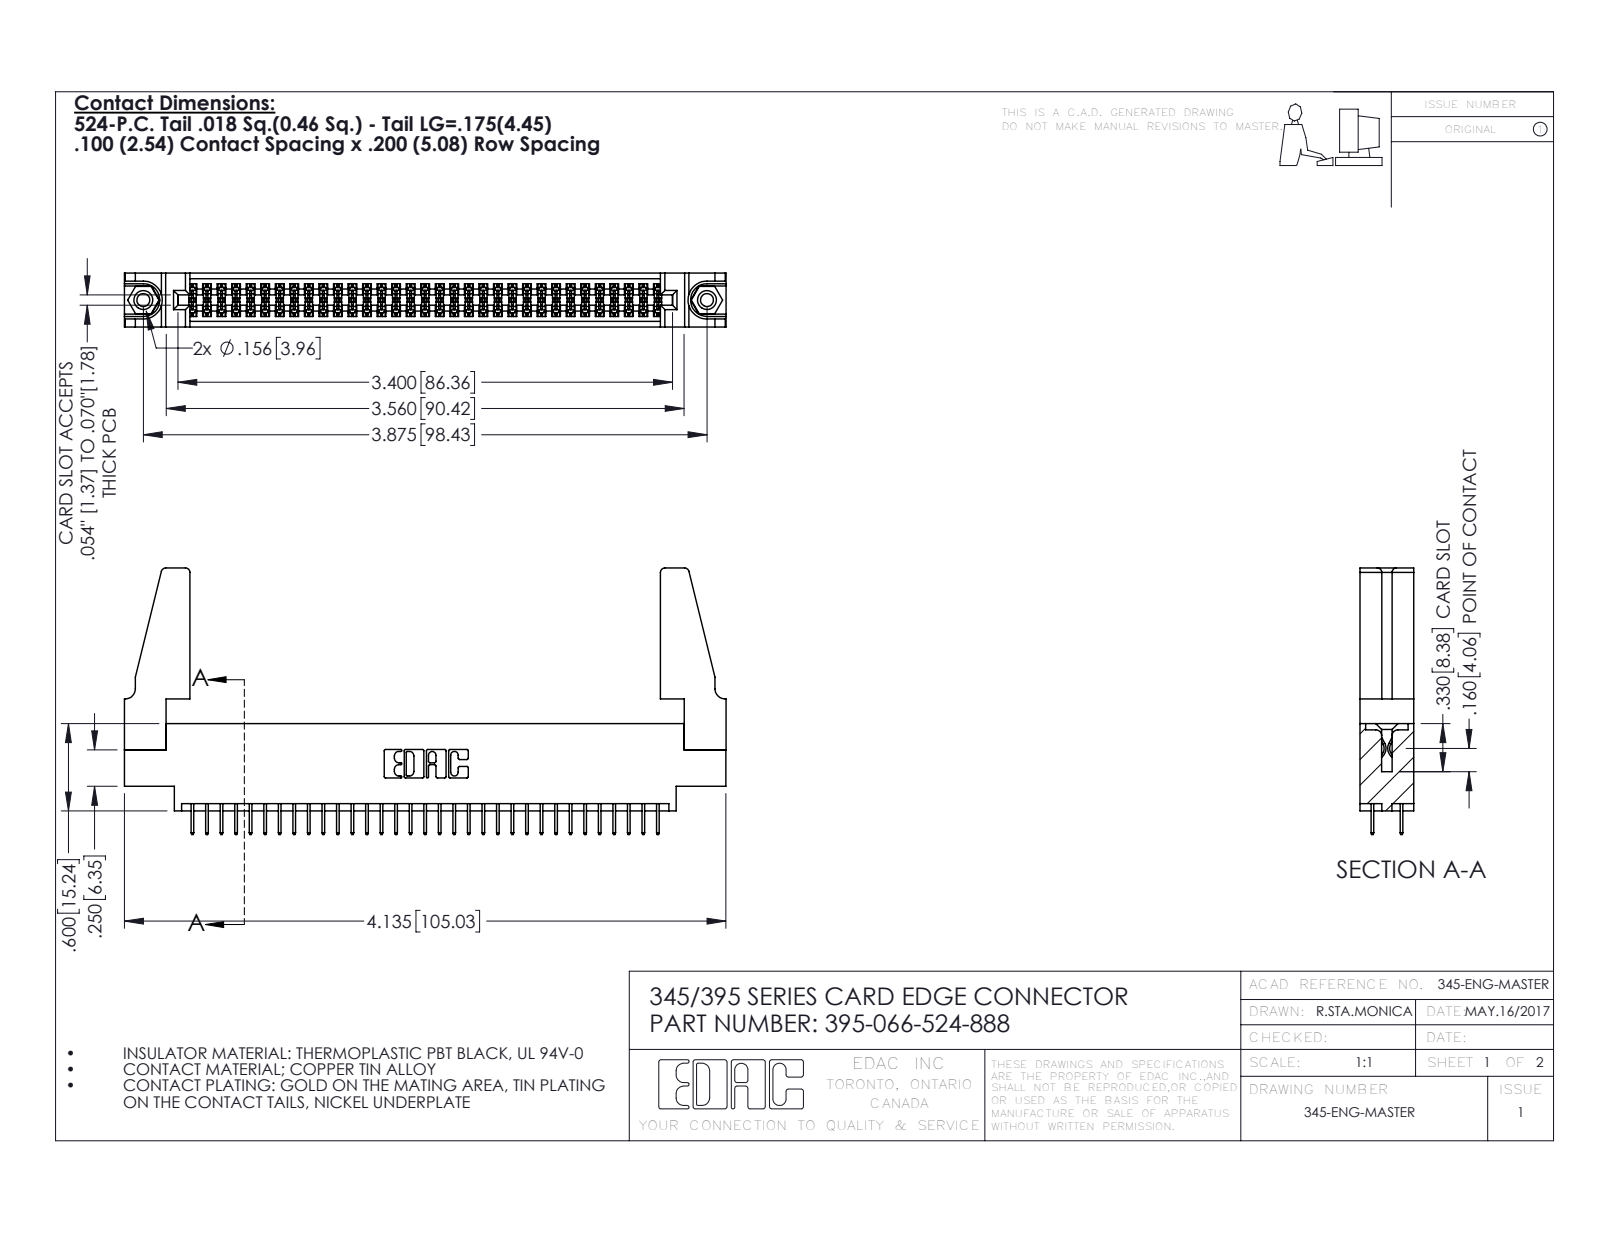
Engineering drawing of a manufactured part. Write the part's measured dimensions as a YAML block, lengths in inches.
part_name: "395-066-524-888; 345-292-001_345-293-124; 345-220-078_345-220-088; 345-250-001_345-250-001-102 (+1 more)"
step_written_by: "SolidWorks 2016 (CONFIG_CONTROL_DESIGN)"
units: inches
bodies: {solids: 71, faces: 3818, planar: 2730, cylindrical: 1072, other: 16}
overall_size: [4.136, 1.832, 0.37]
volume: 0.803
surface_area: 27.08
round_holes:
  - {diameter: 0.089, count: 2}
  - {diameter: 0.125, count: 2}
  - {diameter: 0.156, count: 2}
  - {diameter: 0.064, count: 1}
round_bosses_or_shafts:
  - {diameter: 0.155, count: 2}
partial_cylinders:
  - {radius: 0.006, count: 99}
  - {radius: 0.01, count: 22}
  - {radius: 0.03, count: 8}
  - {radius: 0.007, count: 6}
  - {radius: 0.031, count: 6}
  - {radius: 0.026, count: 3}
  - {radius: 0.014, count: 2}
  - {radius: 0.019, count: 2}
face_to_face_distances: [0.072, 0.37, 0.298, 0.2, 0.098, 0.272, 0.025, 0.225, 0.175, 0.072]
hole_center_spacings: [0.27, 3.64, 3.875]
